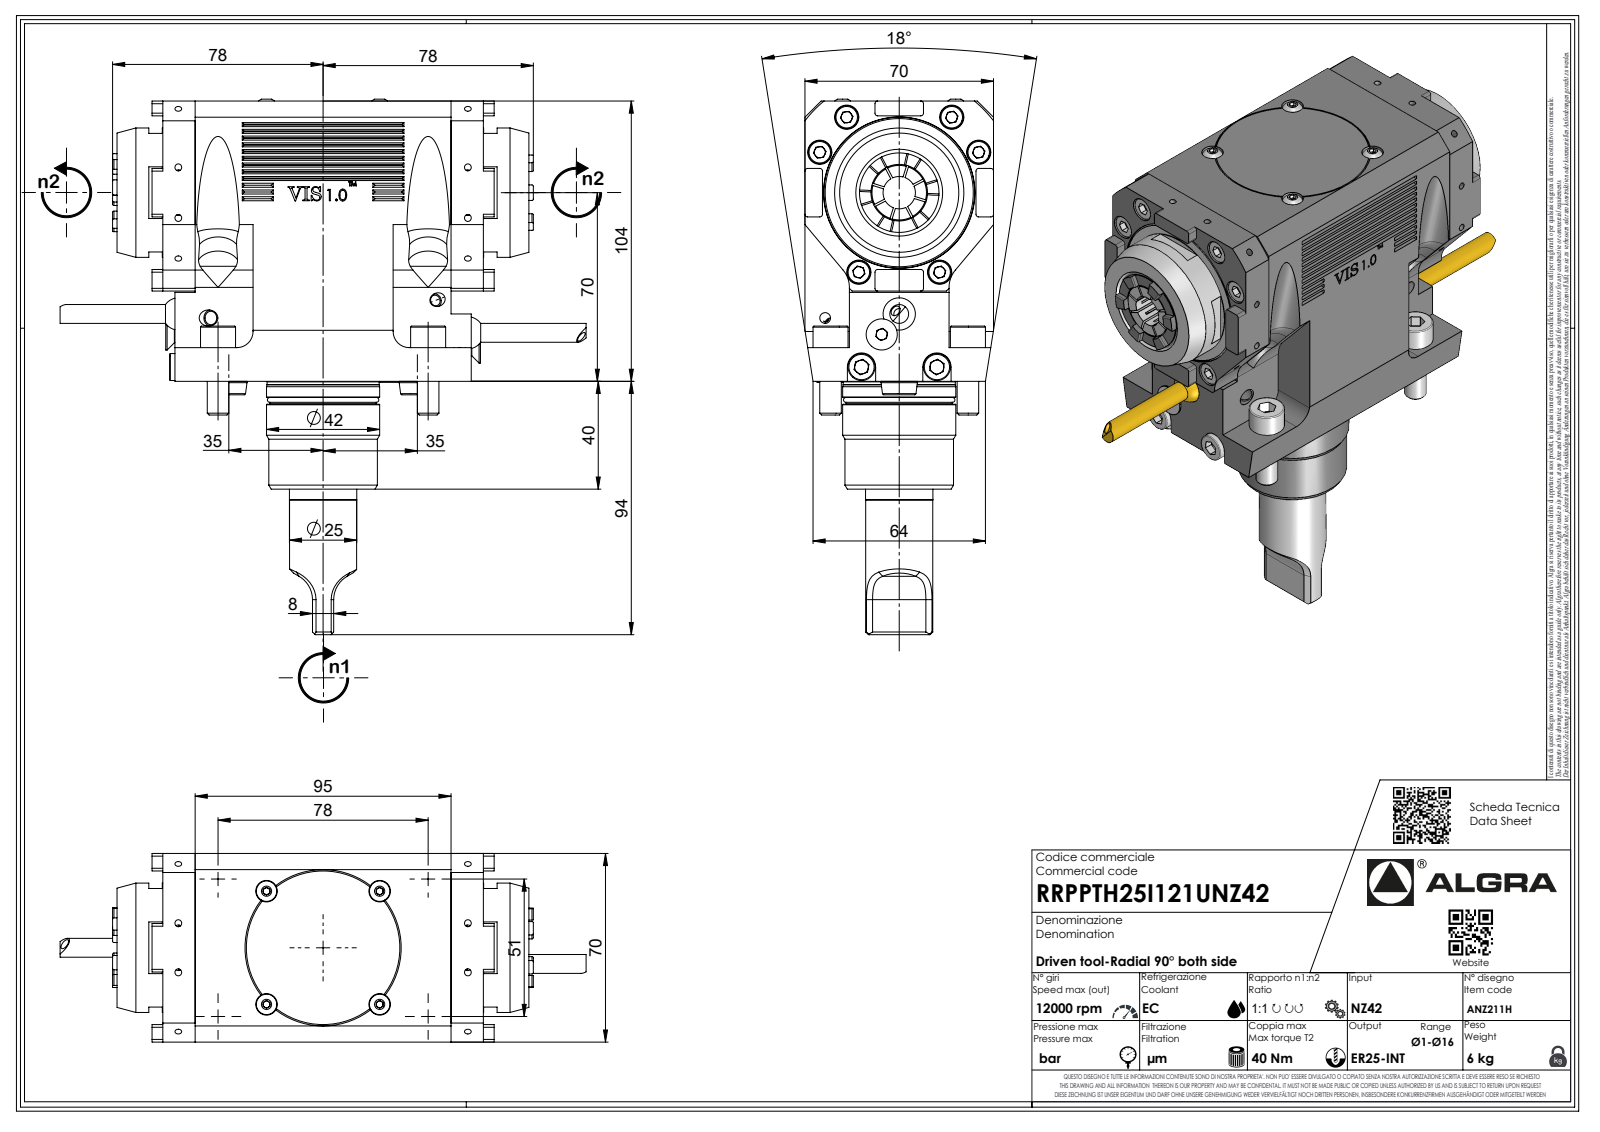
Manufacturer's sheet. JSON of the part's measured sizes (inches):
{"part_name": "RRPPTH25I121UNZ42", "step_written_by": "SolidWorks 2023 (AUTOMOTIVE_DESIGN)", "units": "inches", "bodies": {"solids": 1, "faces": 723, "planar": 416, "cylindrical": 177, "other": 130}, "overall_size": [7.795, 7.688, 2.756], "volume_in3": 54.77, "surface_area_in2": 121.6, "round_holes": [[0.157, 2], [0.083, 1], [0.197, 1]], "round_bosses_or_shafts": [[0.512, 4], [0.315, 4], [0.531, 2], [0.276, 2], [1.89, 1], [1.654, 1], [1.638, 1], [1.587, 1]], "partial_cylinders_radius": [[0.039, 16], [1.378, 16], [0.315, 12], [0.013, 7], [0.02, 7], [0.146, 7], [0.394, 4], [0.079, 2]], "face_to_face_distances": [2.756, 4.094, 1.319, 4.508, 0.177, 0.65, 2.106, 4.685, 1.142, 3.366]}
